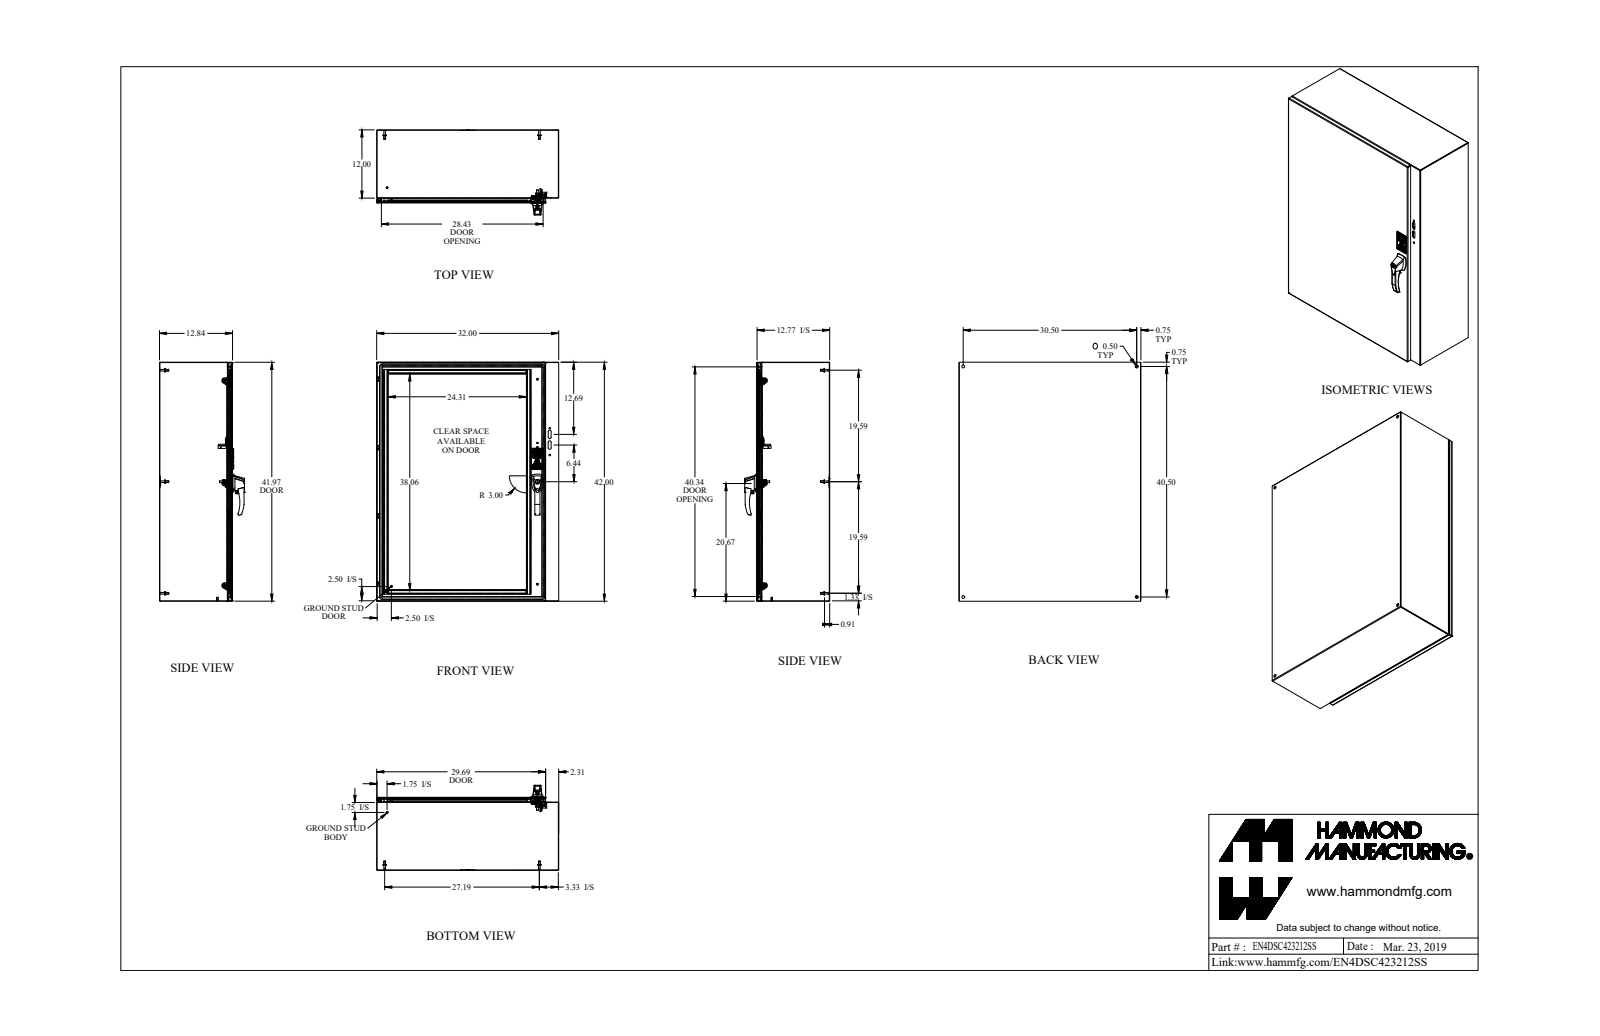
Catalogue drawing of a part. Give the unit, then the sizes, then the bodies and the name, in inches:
Units: inches
Overall size (bounding box): 42 × 32 × 14.952
Round holes (diameter × count): ⌀0.176 ×6, ⌀0.5 ×4, ⌀0.25 ×3, ⌀0.265 ×3, ⌀0.413 ×3, ⌀0.156 ×2, ⌀0.173 ×2, ⌀0.196 ×2, ⌀0.215 ×2, ⌀0.256 ×2, ⌀0.281 ×2, ⌀0.313 ×2
Round bosses / shafts (diameter × count): ⌀0.25 ×9, ⌀0.625 ×6, ⌀0.313 ×6, ⌀0.27 ×6, ⌀0.156 ×6, ⌀0.375 ×5, ⌀1 ×3, ⌀0.63 ×2
Partial cylindrical surfaces — rounded edges, fillets, slot ends (radius × count): R0.043 ×24, R0.081 ×24, R0.036 ×18, R0.108 ×18, R0.25 ×15, R0.03 ×14, R0.125 ×14, R0.006 ×8
Main face-to-face distances: 0.072, 12.765, 12.693, 12.837, 31.928, 41.928, 31.856, 32, 41.856, 42
Hole centre spacings: 18, 1.11, 18, 18.001, 27.596, 30.5, 36.001, 40.5
Volume: 382.2 in³ · Surface area: 10 485 in²
Bodies: 69 solids, 1383 faces (800 planar, 413 cylindrical, 170 other)
Part name (STEP PRODUCT): EN4DSC423212SS
STEP written by: SolidWorks 2019 (AUTOMOTIVE_DESIGN)
